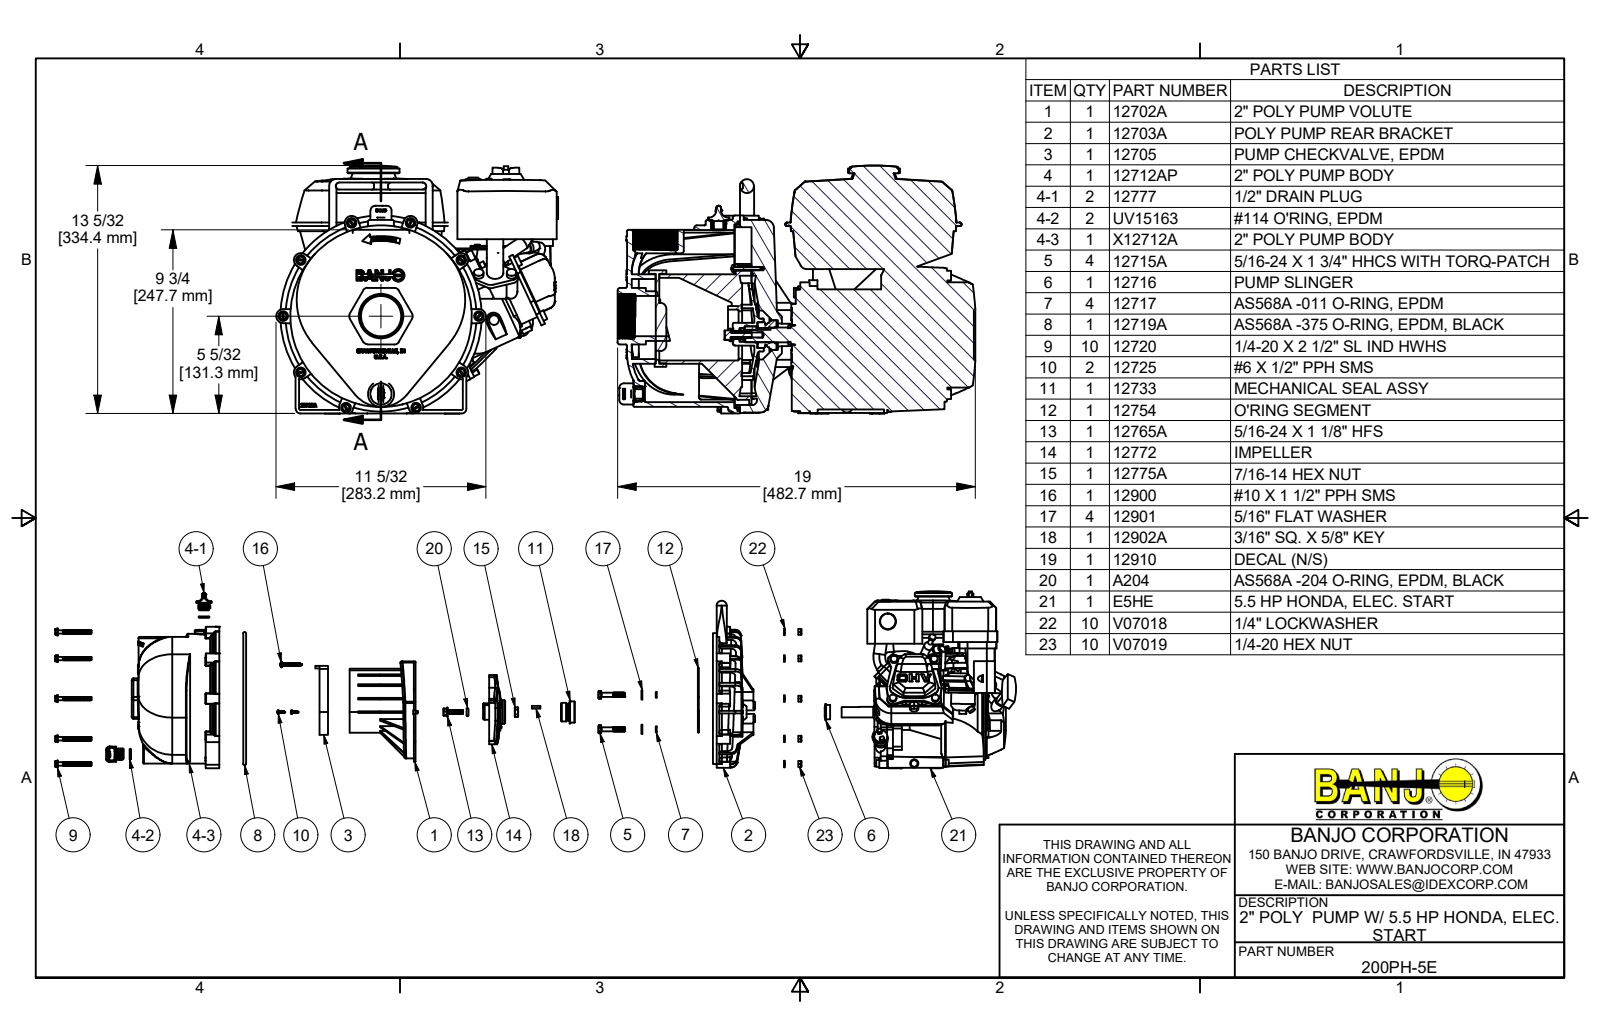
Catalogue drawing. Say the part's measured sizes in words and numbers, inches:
The part is named "200PH-5E; 12703A; 12712AP; X12712A (+8 more)". Its 3-D file was written by "Autodesk Inventor 2019 (AUTOMOTIVE_DESIGN)". It is 86 solids with 8947 faces: 2801 planar, 2279 cylindrical and 3867 other. Overall it measures 19.762 by 14.984 by 14.538 inches. Its volume is 1 147 cubic inches and its surface area 2 847 square inches. Round holes: 10 of diameter 0.196, 10 of diameter 0.252, 10 of diameter 0.27, 7 of diameter 0.22, 4 of diameter 0.344, 4 of diameter 0.469, 4 of diameter 0.815, 2 of diameter 0.113, 2 of diameter 0.115, 2 of diameter 0.205, 2 of diameter 0.25, 2 of diameter 0.5. Round bosses or shafts: 80 of diameter 0.276, 10 of diameter 0.52, 10 of diameter 0.489, 10 of diameter 0.25, 6 of diameter 0.512, 6 of diameter 0.192, 4 of diameter 0.688, 4 of diameter 0.313. Partial cylindrical surfaces (rounded edges, fillets, slot ends): 116 of radius 0.03, 33 of radius 0.25, 26 of radius 0.008, 24 of radius 0.079, 24 of radius 0.187, 23 of radius 0.06, 23 of radius 0.125, 13 of radius 0.015. The main face-to-face distances are 0.18, 0.2, 0.037, 0.163, 2.88, 1.589, 0.11, 0.25, 0.5, 1. The hole center spacings are 5.2, 1.81, 2.56, 3.128, 6.15, 8.387, 10.4, 1.31.
